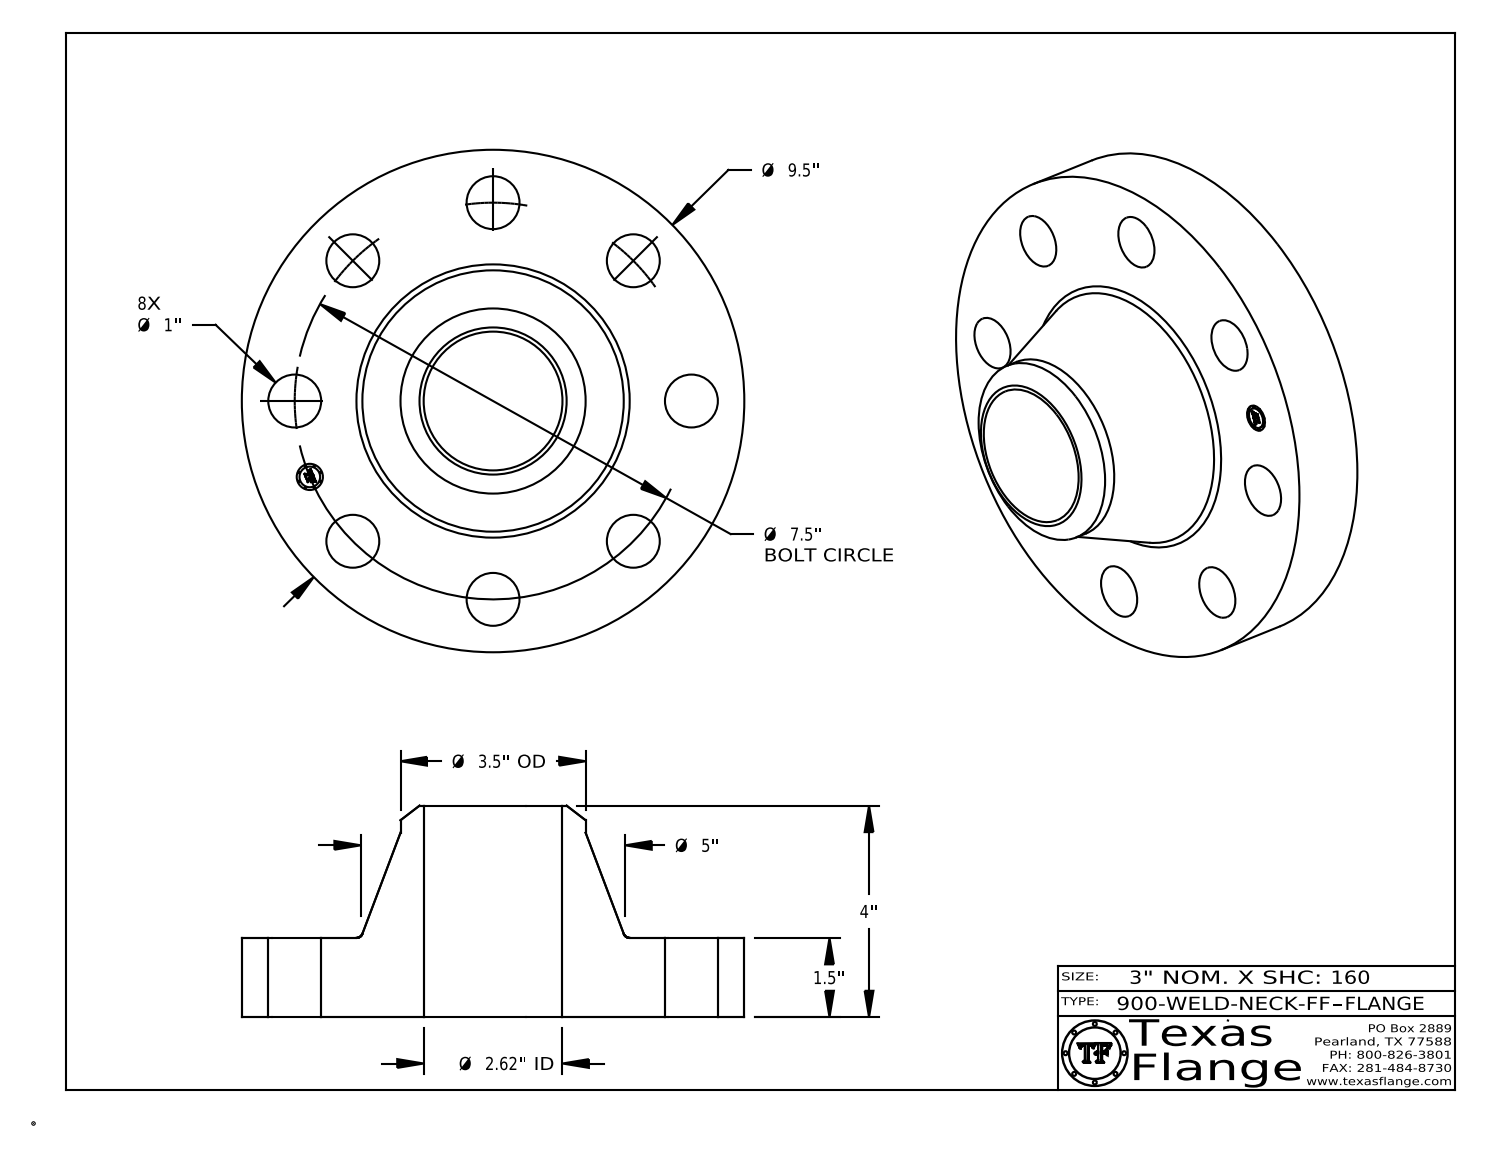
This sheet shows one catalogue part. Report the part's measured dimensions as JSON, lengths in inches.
{"part_name": "900-WELD-NECK-FF", "step_written_by": "CATIA V5 STEP AP214 (AUTOMOTIVE_DESIGN)", "units": "inches", "bodies": {"solids": 1, "faces": 416, "planar": 368, "cylindrical": 42, "other": 6}, "overall_size": [9.5, 9.5, 4], "volume_in3": 108.2, "surface_area_in2": 255.5, "round_holes": [[1, 8], [0.495, 1], [2.624, 1]], "round_bosses_or_shafts": [[0.03, 8], [9.5, 1], [3.5, 1], [0.39, 1]], "face_to_face_distances": [1.5, 4, 2.5, 0.015, 1.485, 2.515, 0.148, 0.145, 0.027, 0.096], "hole_center_spacings": [3.75, 2.87, 5.303, 6.929, 1.463, 6.236, 7.356, 7.5]}
